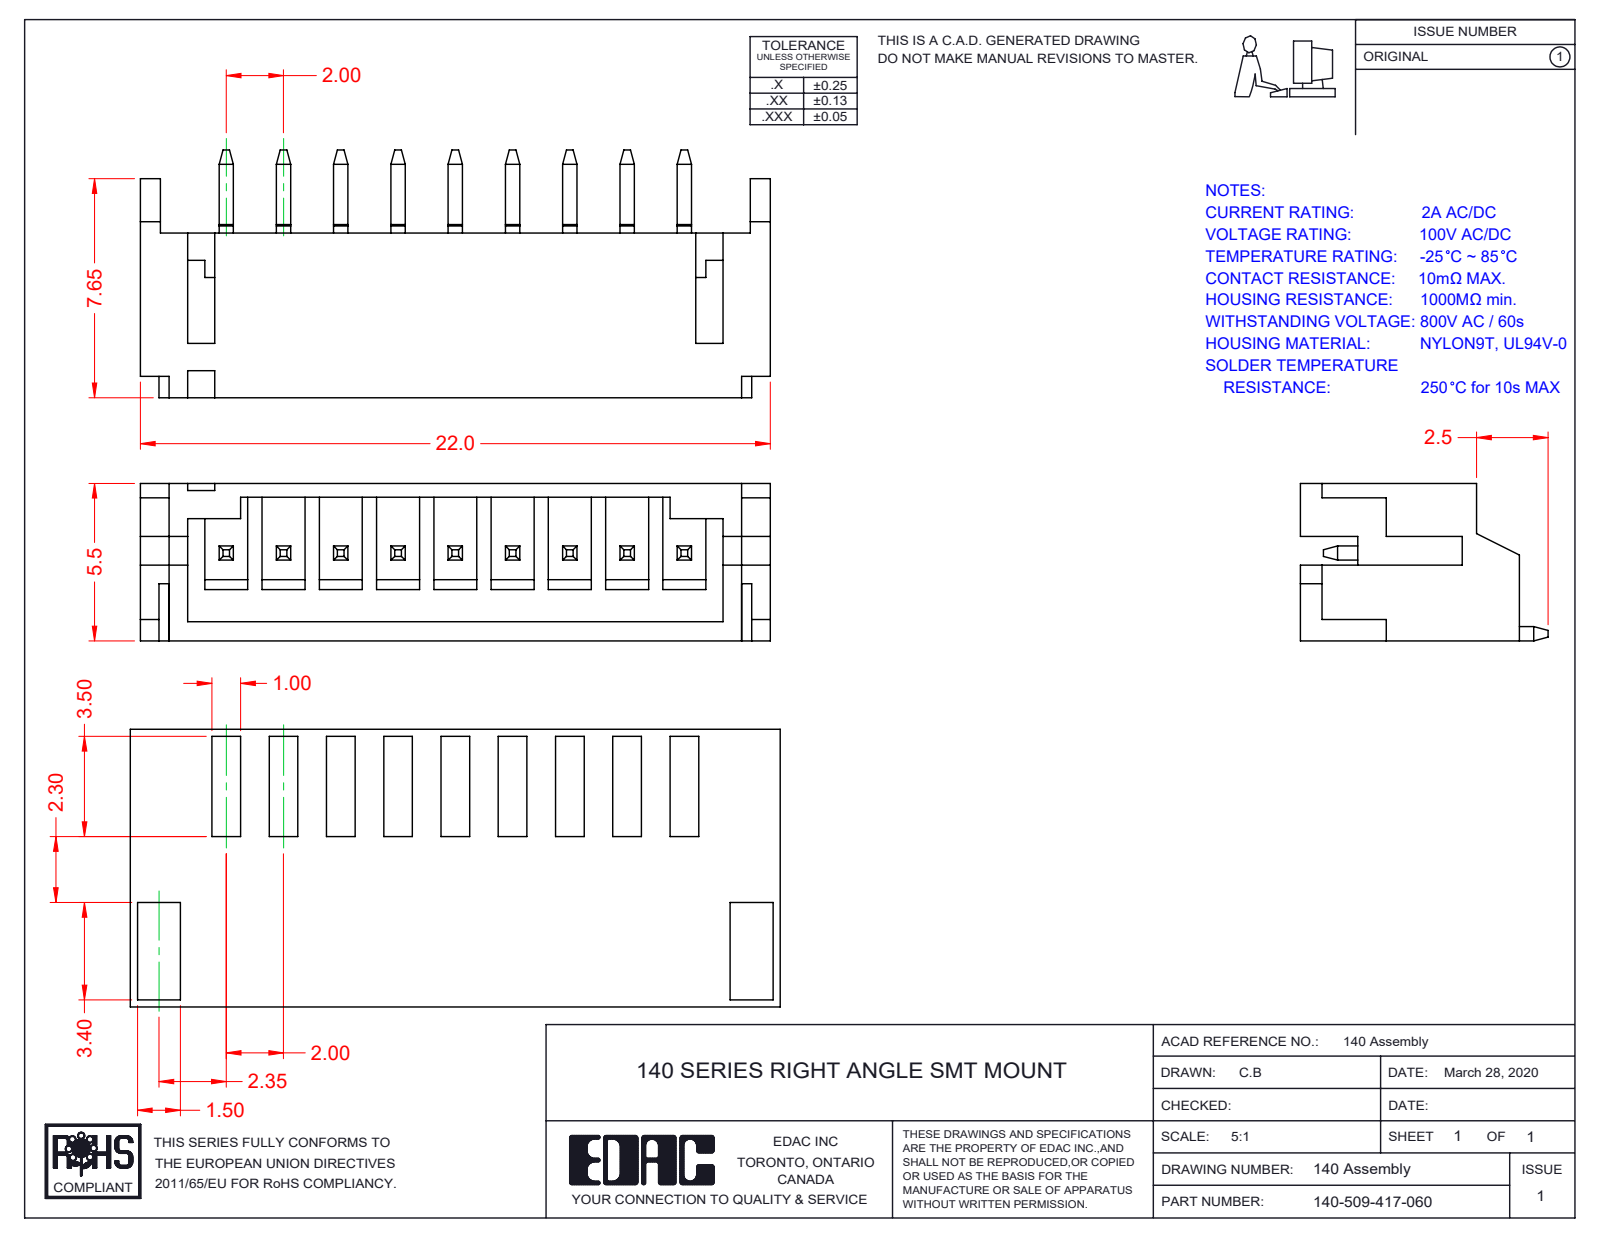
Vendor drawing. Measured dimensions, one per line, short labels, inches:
name: 140-509-417-060; RA SMT Pad; RA SMT Housing_509; RA SMT Contact
written by: SolidWorks 2016 (CONFIG_CONTROL_DESIGN)
unit: in
bodies: 12 solids, 494 faces (458 planar, 36 cylindrical, 0 other)
size: 0.866 × 0.341 × 0.217
volume: 0.019 in³; area: 1.77 in²
rounds: 2× R0.022
face distances: 0.217, 0.026, 0.026, 0.19, 0.02, 0.171, 0.039, 0.198, 0.019, 0.037
